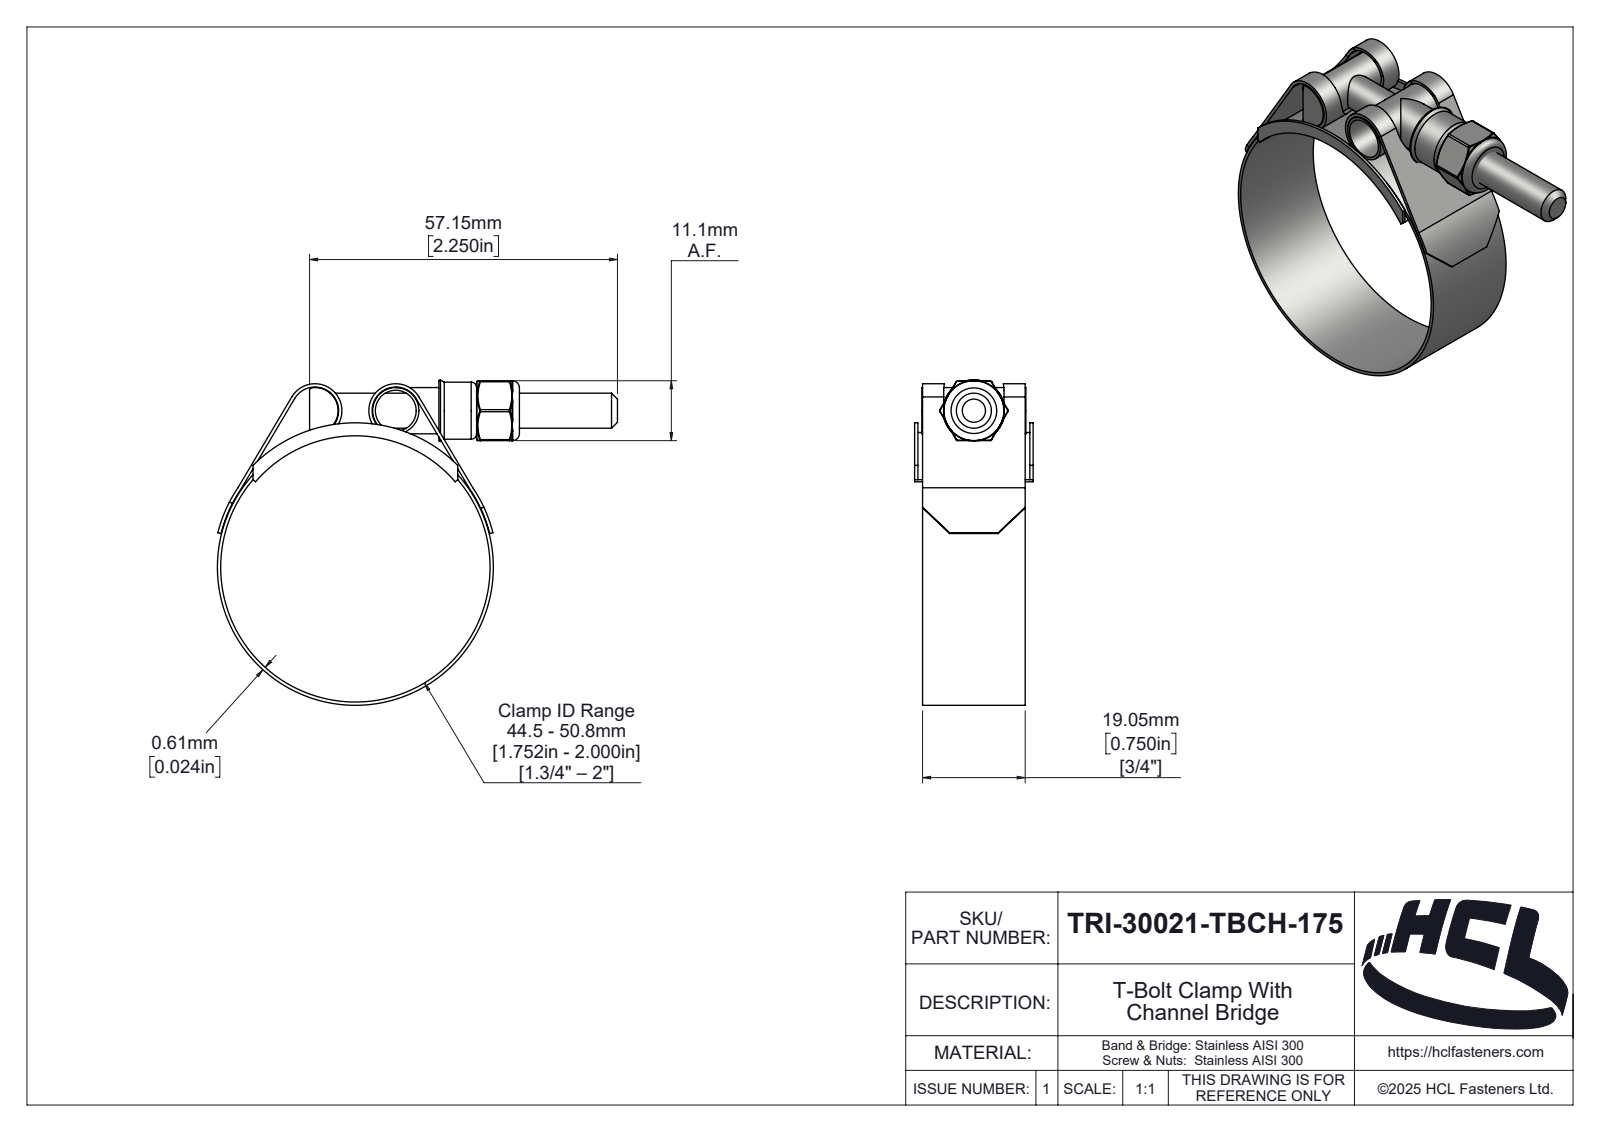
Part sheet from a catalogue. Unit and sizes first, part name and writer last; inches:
Units: inches
Overall size (bounding box): 2.924 × 2.377 × 0.866
Round holes (diameter × count): ⌀0.213 ×1, ⌀0.25 ×1, ⌀0.256 ×1, ⌀0.298 ×1, ⌀1.969 ×1
Round bosses / shafts (diameter × count): ⌀0.338 ×2, ⌀2.017 ×1, ⌀0.417 ×1
Partial cylindrical surfaces — rounded edges, fillets, slot ends (radius × count): R0.015 ×6, R0.02 ×2, R0.173 ×2, R0.197 ×2, R0.22 ×2, R0.023 ×1, R0.095 ×1, R0.119 ×1
Main face-to-face distances: 0.024, 0.058, 0.808, 0.029, 0.842, 0.034, 0.784, 0.75, 0.437, 0.866
Hole centre spacings: 1.181
Volume: 0.42 in³ · Surface area: 22.85 in²
Bodies: 6 solids, 338 faces (50 planar, 126 cylindrical, 162 other)
Part name (STEP PRODUCT): TRI-30021-TBCH-175
STEP written by: SolidWorks 2025 (AUTOMOTIVE_DESIGN)
